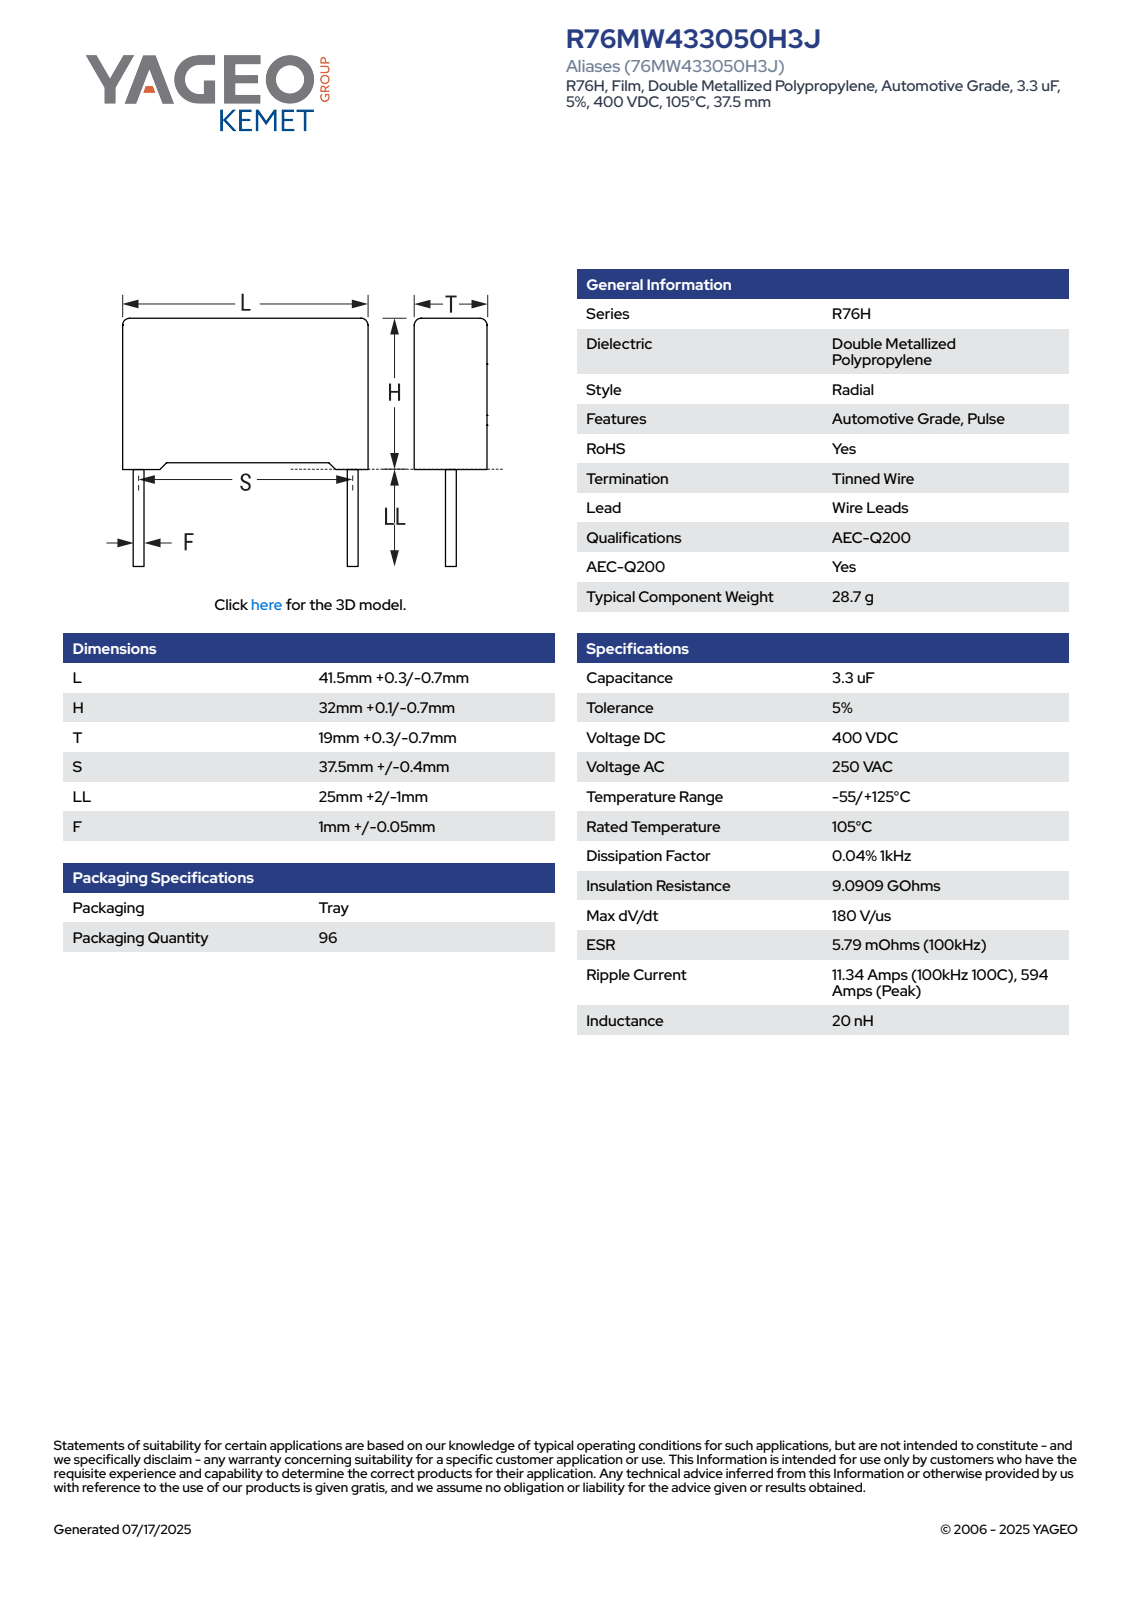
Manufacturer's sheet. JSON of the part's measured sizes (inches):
{"part_name": "CFR_RB2R76_41.5X32X19_L41.8H32.1T19.3S37.5LL27F1.05", "step_written_by": "SolidWorks 2014 (AUTOMOTIVE_DESIGN)", "units": "inches", "bodies": {"solids": 4, "faces": 85, "planar": 77, "cylindrical": 8, "other": 0}, "overall_size": [2.327, 1.646, 0.76], "volume_in3": 1.535, "surface_area_in2": 8.975, "round_bosses_or_shafts": [[0.041, 2]], "partial_cylinders_radius": [[0.02, 4]], "face_to_face_distances": [0.76, 1.22, 1.646, 0.014, 1.234, 0.03, 0.044, 1.264, 0.055, 0.76]}
